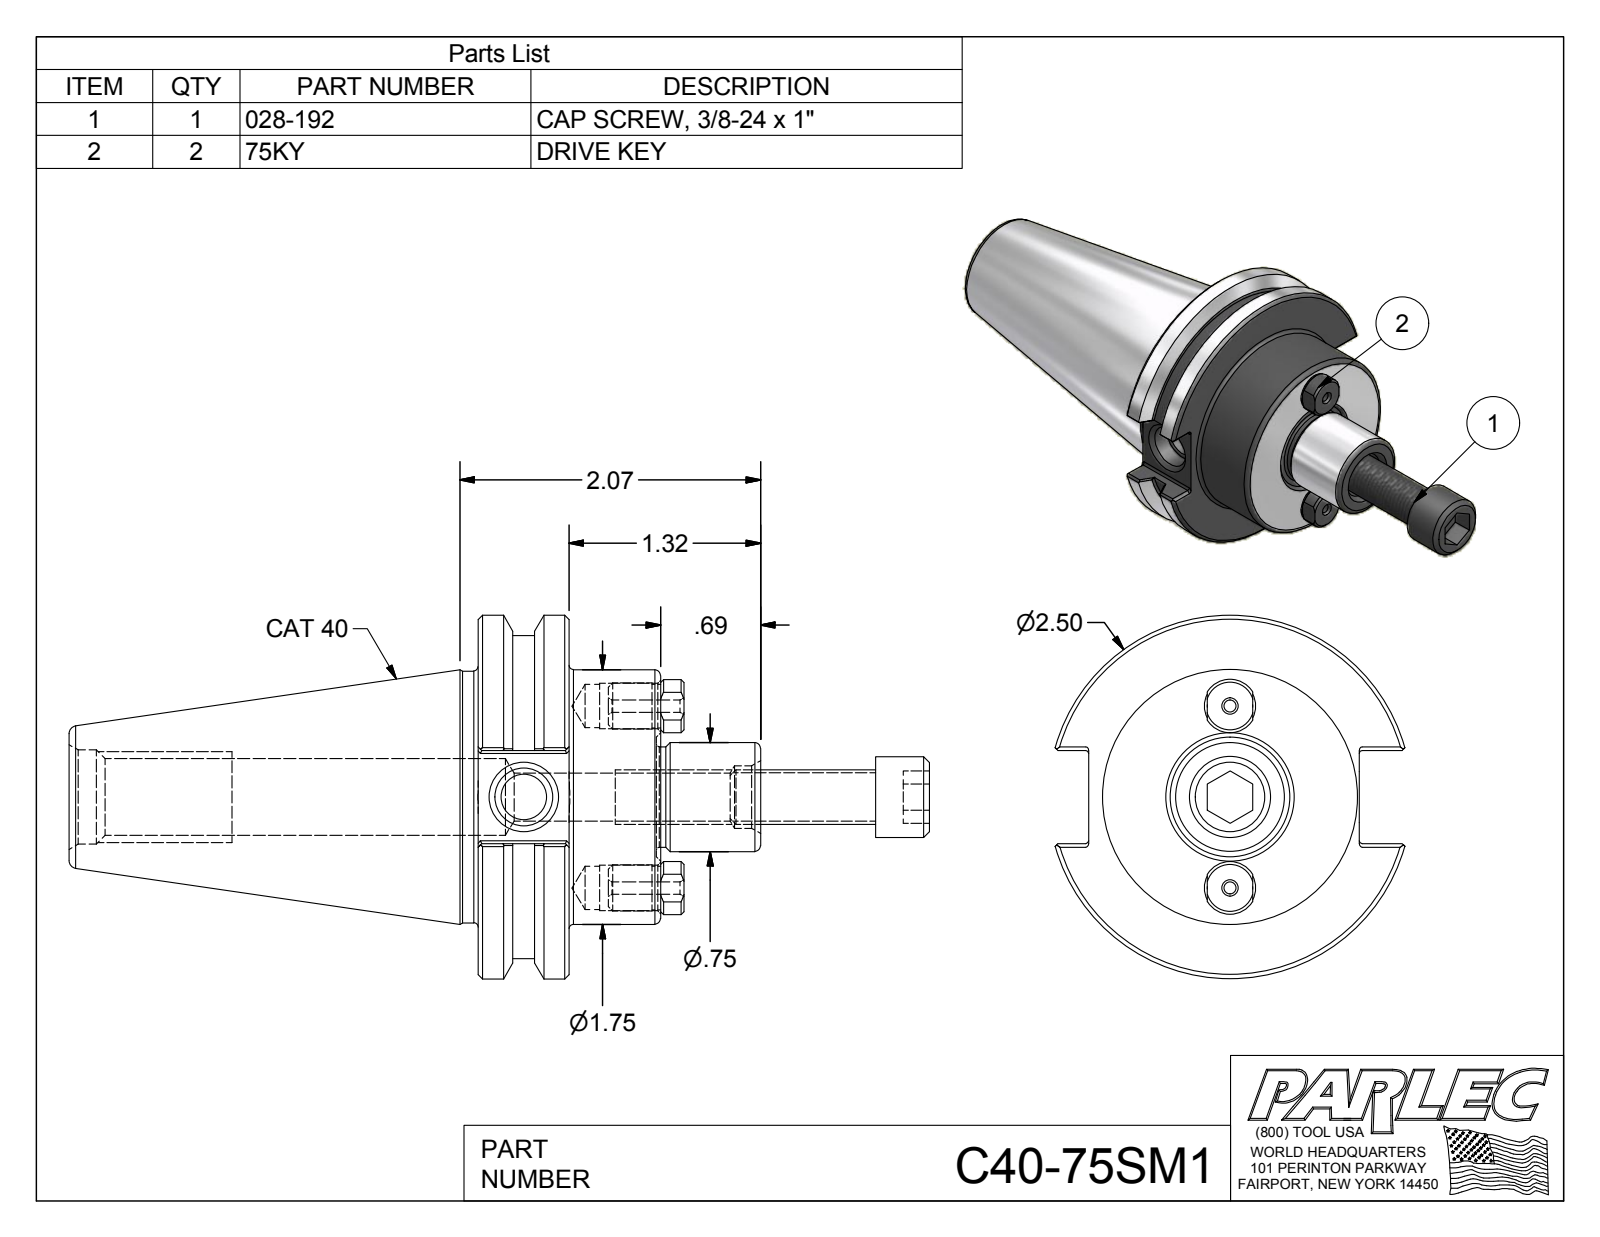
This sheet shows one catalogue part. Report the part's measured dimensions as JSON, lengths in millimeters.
{"part_name": "C40-75SM1; C40-75SM1-1; 75KY; 028-192", "step_written_by": "Autodesk Inventor 2012 (AUTOMOTIVE_DESIGN)", "units": "millimeters", "bodies": {"solids": 4, "faces": 154, "planar": 57, "cylindrical": 44, "other": 53}, "overall_size": [150.3, 63.5, 61.1], "volume_mm3": 131800, "surface_area_mm2": 27590, "round_holes": [[2.1, 2], [7.5, 2], [7.9, 2], [8, 1], [8.4, 1], [10.1, 1], [10.9, 1], [13.4, 1], [16.5, 1]], "round_bosses_or_shafts": [[8.1, 2], [7.6, 2], [63.5, 1], [56.4, 1], [44.5, 1], [43.9, 1], [19.1, 1], [17.5, 1]], "partial_cylinders_radius": [[0.5, 12], [4.6, 2]], "face_to_face_distances": [15.9, 31.9, 16, 33.5, 20.1, 16.3, 47.2, 71.4, 87.3, 103.3], "hole_center_spacings": [15.9, 31.8]}
